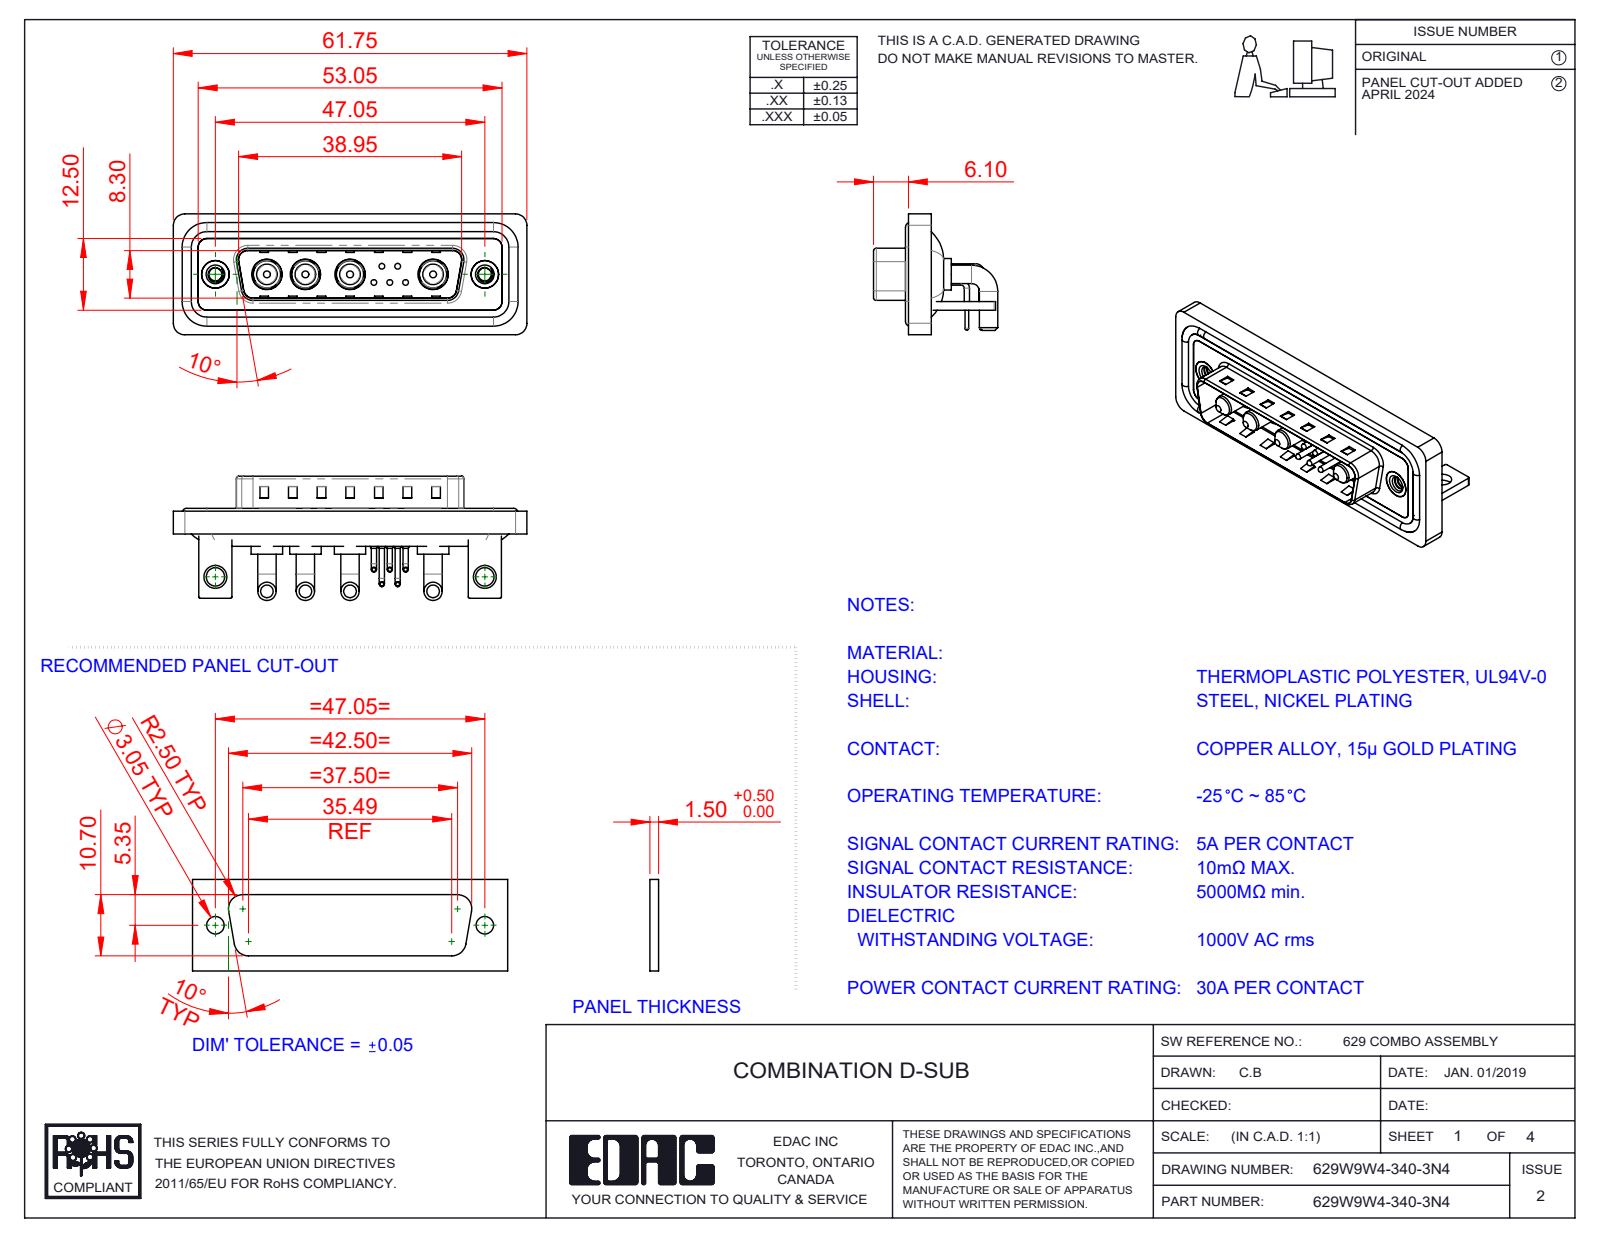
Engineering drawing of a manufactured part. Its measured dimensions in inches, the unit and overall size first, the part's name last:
Units: inches
Overall size (bounding box): 2.431 × 0.854 × 0.831
Round holes (diameter × count): ⌀0.03 ×5, ⌀0.063 ×5, ⌀0.079 ×5, ⌀0.191 ×4, ⌀0.209 ×4, ⌀0.089 ×2, ⌀0.126 ×2, ⌀0.157 ×2, ⌀0.189 ×2, ⌀0.197 ×2
Round bosses / shafts (diameter × count): ⌀0.035 ×10, ⌀0.126 ×8, ⌀0.059 ×5, ⌀0.039 ×5, ⌀0.026 ×5, ⌀0.217 ×4, ⌀0.205 ×4, ⌀0.187 ×4
Partial cylindrical surfaces — rounded edges, fillets, slot ends (radius × count): R0.079 ×19, R0.059 ×18, R0.01 ×16, R0.02 ×9, R0.063 ×8, R0.04 ×5, R0.024 ×4, R0.026 ×4
Main face-to-face distances: 0.016, 0.059, 0.031, 0.114, 0.083, 0.043, 0.146, 0.161, 0.177, 0.063
Hole centre spacings: 0.124, 0.109, 0.198, 0.571, 1.852, 0.109, 0.173, 0.174
Volume: 0.494 in³ · Surface area: 20.21 in²
Bodies: 22 solids, 1245 faces (589 planar, 470 cylindrical, 186 other)
Part name (STEP PRODUCT): Power Pin_30A RA; 629Combo Stabilizer Bracket; 629Combo Threaded Rivet_3; 629Combo Contact Row 2 (+6 more)
STEP written by: SolidWorks 2023 (CONFIG_CONTROL_DESIGN)
